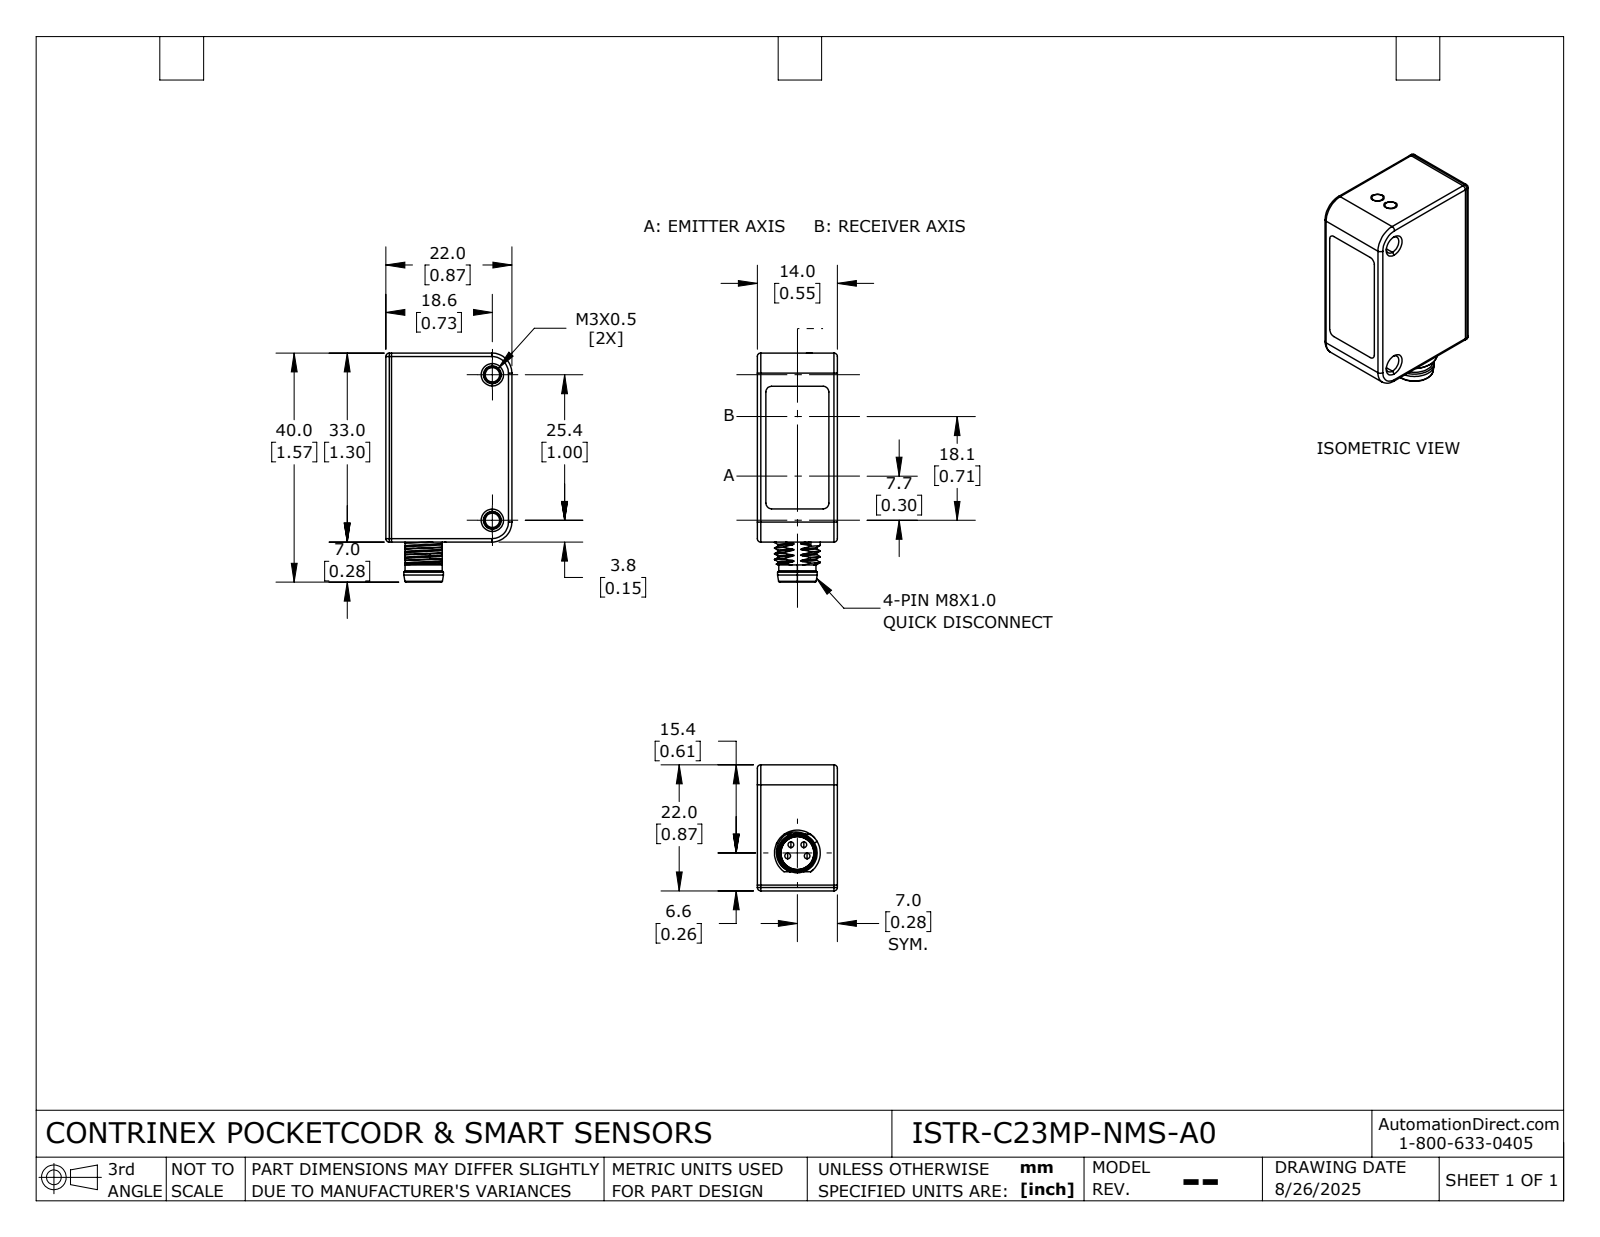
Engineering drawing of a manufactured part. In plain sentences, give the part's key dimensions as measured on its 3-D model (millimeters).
The part is named "ISTR-C23MP-NMS-A0". Its 3-D file was written by "SolidWorks 2024 (AUTOMOTIVE_DESIGN)". It is 1 solid with 162 faces: 27 planar, 58 cylindrical and 77 other. Overall it measures 40 by 22 by 14 millimeters. Its volume is 10 000 cubic millimeters and its surface area 3 551 square millimeters. Round holes: 2 of diameter 2.5, 2 of diameter 3.1, 1 of diameter 5.8. Round bosses or shafts: 4 of diameter 1, 1 of diameter 6.9, 1 of diameter 6.5. Partial cylindrical surfaces (rounded edges, fillets, slot ends): 10 of radius 0.6, 2 of radius 3.5, 1 of radius 4. The main face-to-face distances are 14, 22, 33, 1, 2, 32.5, 0.6, 34, 35, 1.5. The hole center spacings are 25.4.
